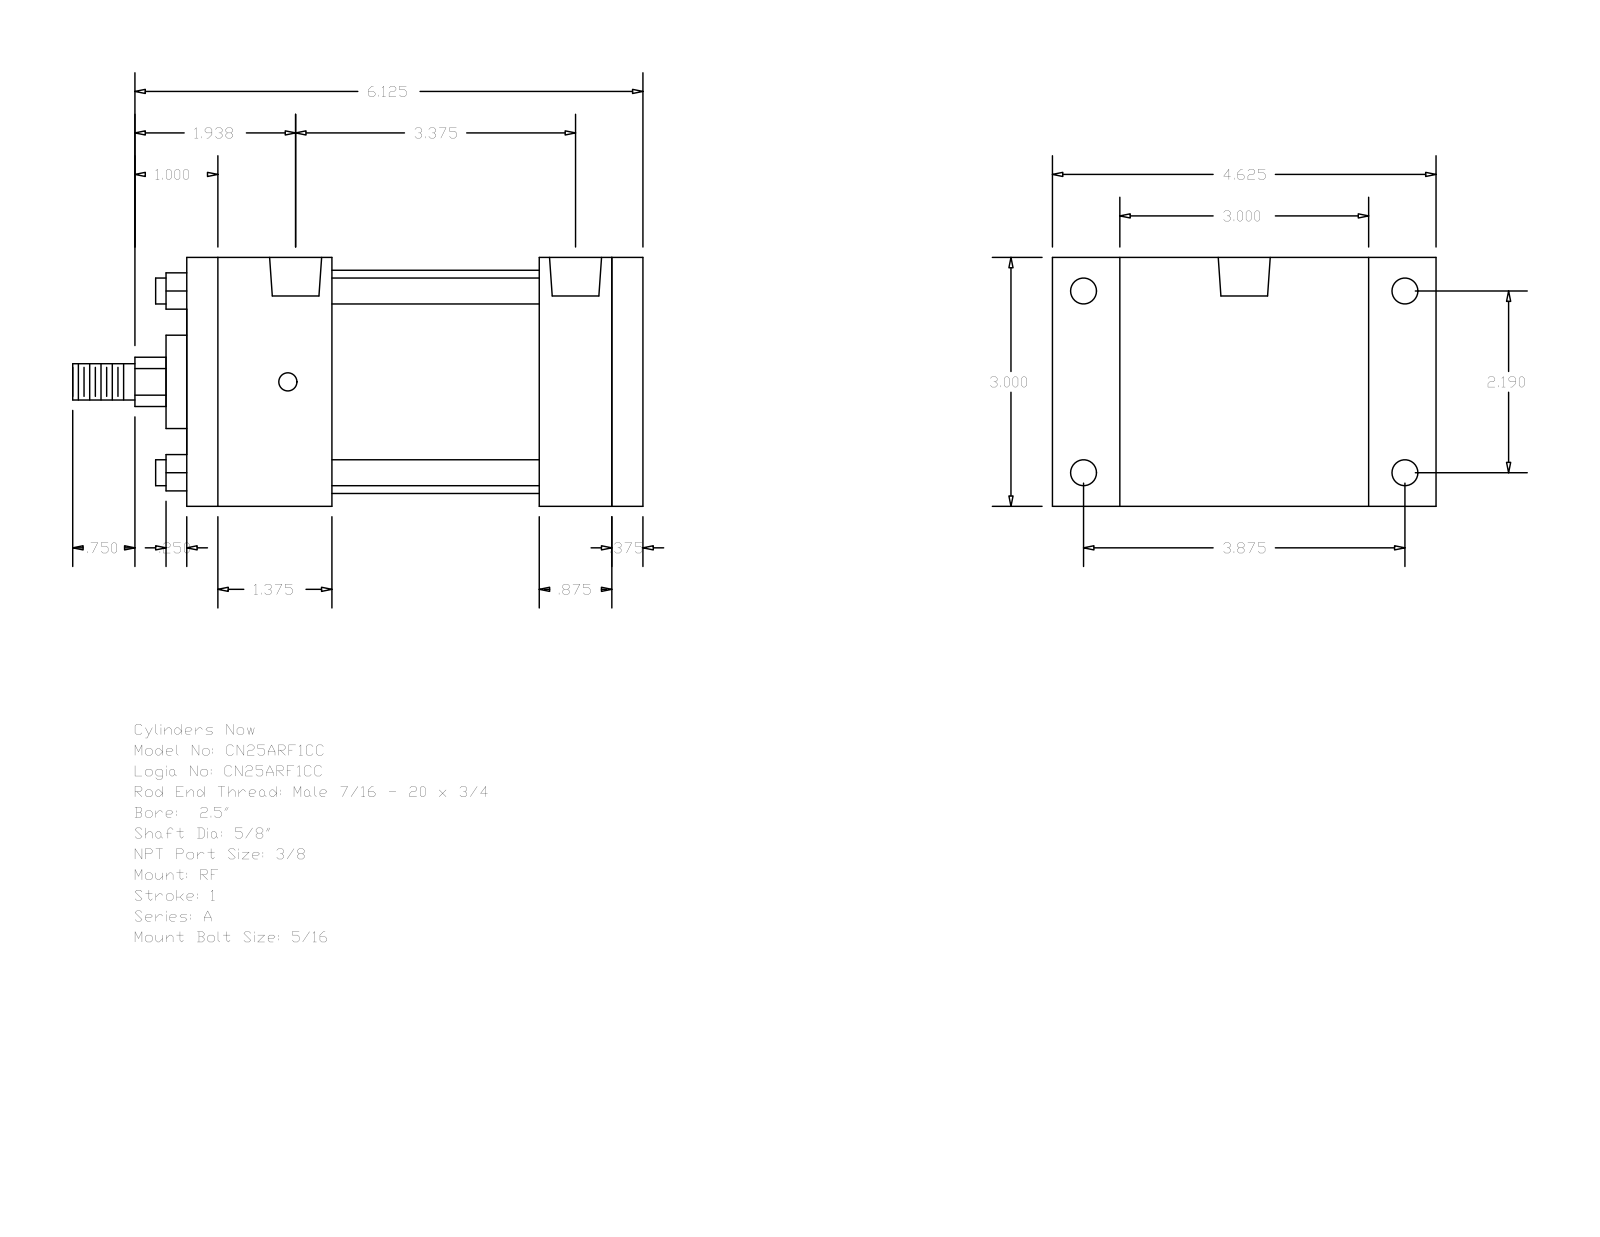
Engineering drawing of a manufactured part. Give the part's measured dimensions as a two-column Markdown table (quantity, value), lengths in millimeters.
| quantity | value |
| --- | --- |
| part name | A_RF__0250_0.625 |
| STEP written by | GSSL Pune (CONFIG_CONTROL_DESIGN) |
| units | millimeters |
| bodies | 0 solids, 92 faces (64 planar, 28 cylindrical, 0 other) |
| overall size | 174.62 × 117.47 × 76.2 |
| round holes (diameter × count) | 5.56 × 4, 7.94 × 4, 15.93 × 2 |
| round bosses / shafts (diameter × count) | 7.94 × 4, 68.33 × 1, 28.57 × 1, 15.88 × 1, 11.11 × 1 |
| partial cylindrical surfaces (radius × count) | 7.54 × 1 |
| main face-to-face distances | 76.2, 139.69, 130.17, 9.52, 44.45, 95.24, 107.95, 63.5, 85.72, 22.22 |
| hole center spacings | 2.38, 55.62, 88.11, 90.49, 98.42, 113.05, 85.73 |
